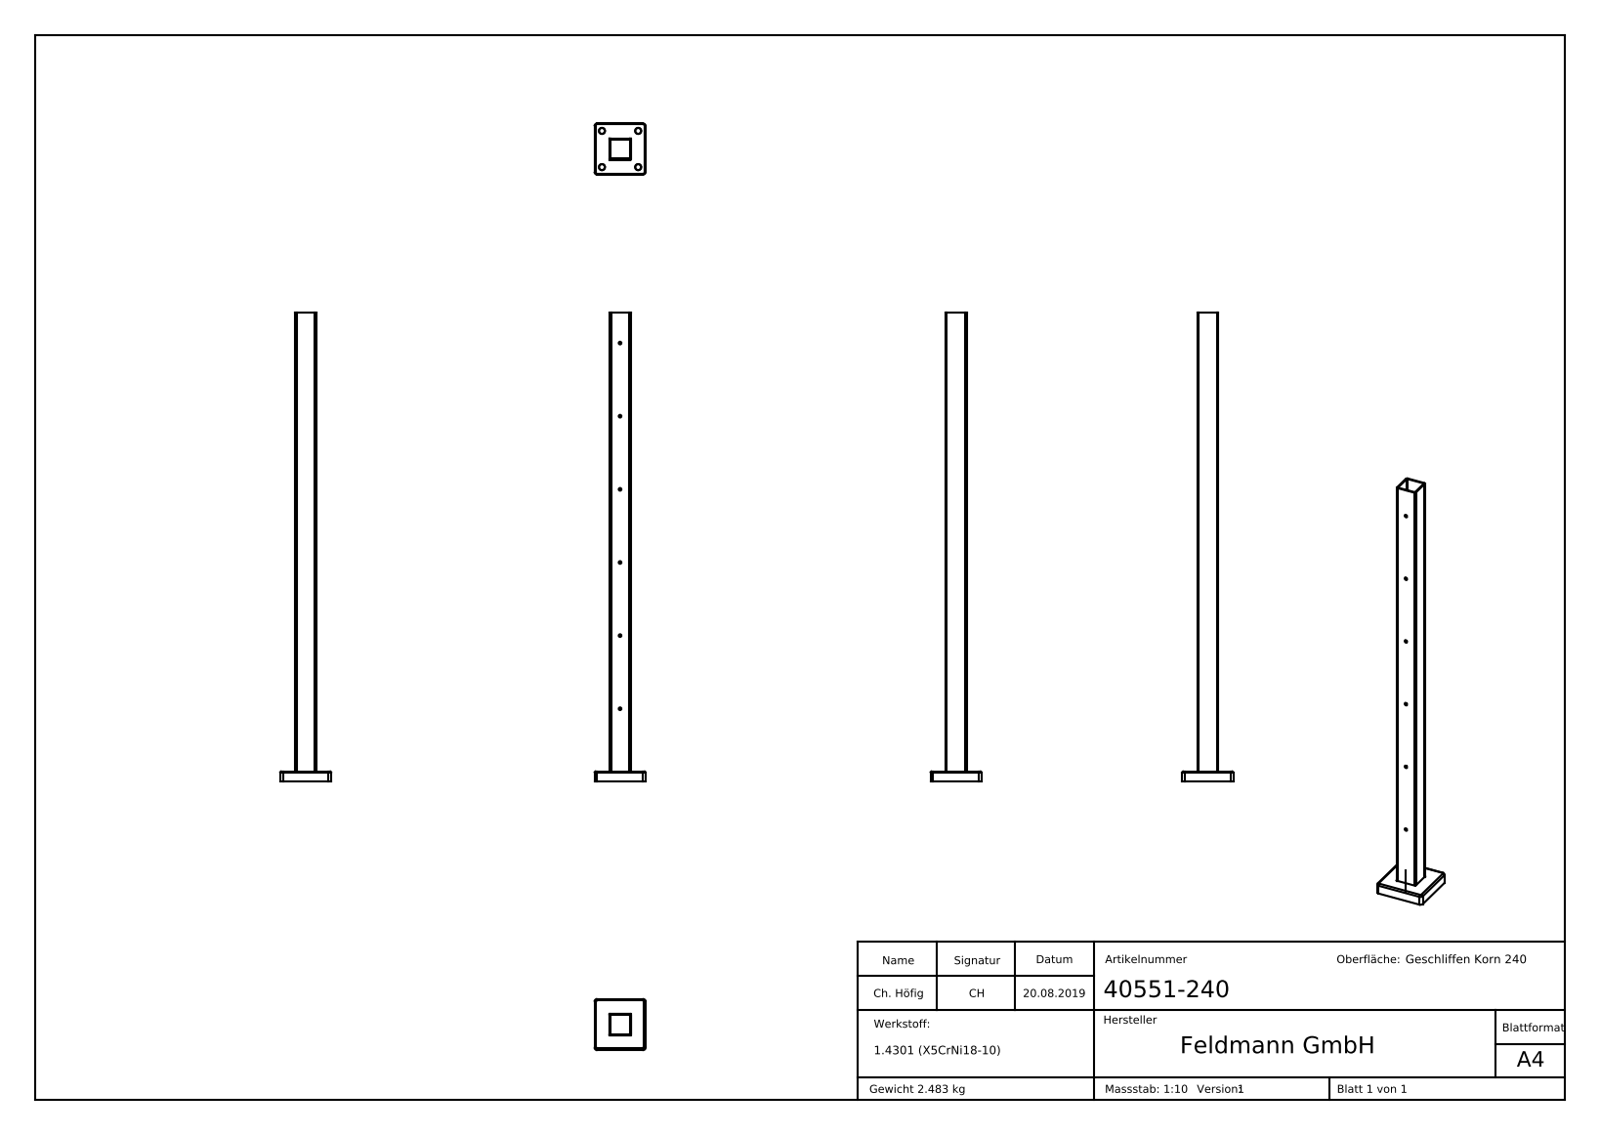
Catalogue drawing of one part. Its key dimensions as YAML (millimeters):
part_name: "54208-240_54208-240; 40551-240; 51250-240_51250-240; 405XX-240 Teil1_40551-240 Teil1"
step_written_by: "SolidWorks 2015 (CONFIG_CONTROL_DESIGN)"
units: millimeters
bodies: {solids: 3, faces: 115, planar: 35, cylindrical: 56, other: 24}
overall_size: [880, 96, 96]
volume: 314247
surface_area: 307877
round_holes:
  - {diameter: 5, count: 6}
  - {diameter: 11, count: 4}
partial_cylinders:
  - {radius: 2, count: 8}
  - {radius: 3, count: 8}
  - {radius: 0.5, count: 4}
  - {radius: 1, count: 4}
  - {radius: 1.5, count: 4}
  - {radius: 4, count: 4}
  - {radius: 5, count: 4}
face_to_face_distances: [2, 38, 40, 36, 1, 28, 66, 19, 20, 6]
hole_center_spacings: [137.28, 68, 274.56, 411.84, 96.17, 549.12, 686.4]
